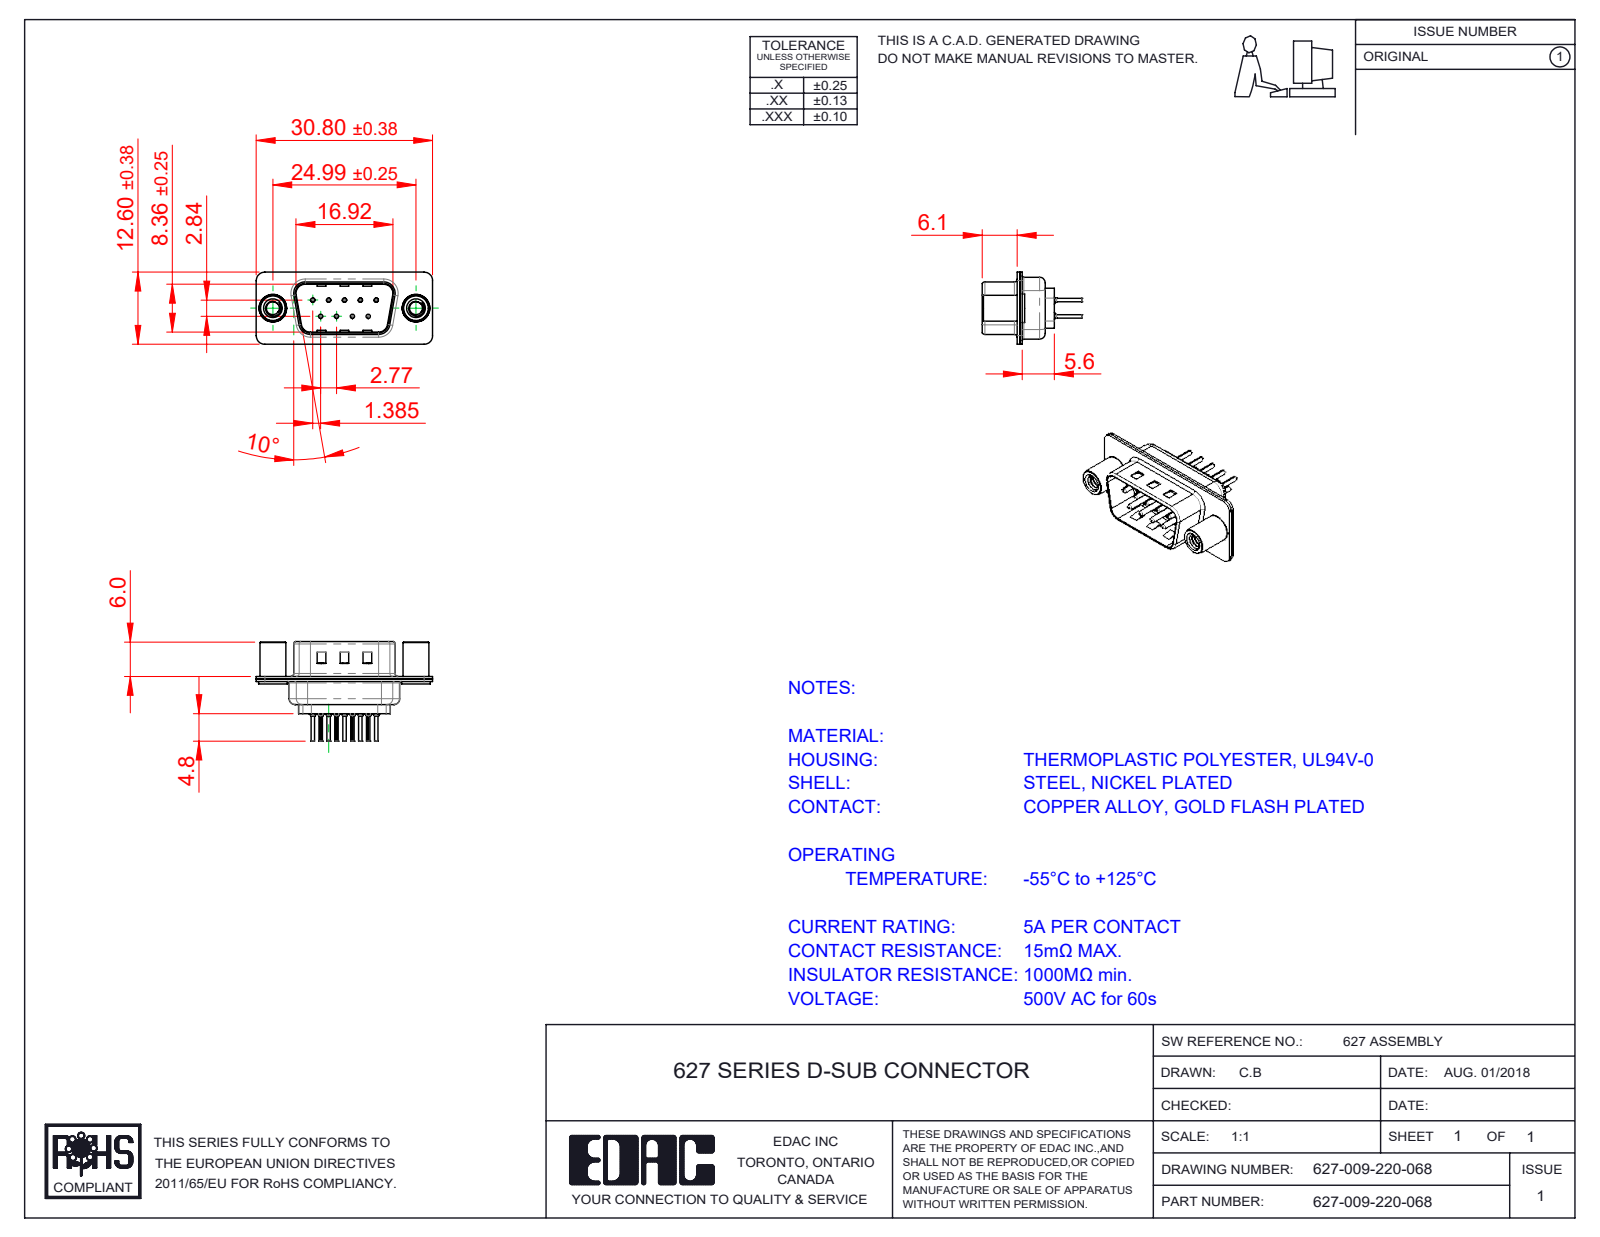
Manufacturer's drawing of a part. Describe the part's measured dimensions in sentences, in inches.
The part is named "627 Contact Row 1_20L; 627 Shell Rear_09 Contacts; 627 4-40 Threaded Standoff; 627 Housing_09 LP (+3 more)". Its 3-D file was written by "SolidWorks 2020 (CONFIG_CONTROL_DESIGN)". It is 14 solids with 1220 faces: 325 planar, 490 cylindrical and 405 other. Overall it measures 1.213 by 0.681 by 0.496 inches. Its volume is 0.084 cubic inches and its surface area 6.4 square inches. Round holes: 9 of diameter 0.008, 9 of diameter 0.014, 9 of diameter 0.043, 9 of diameter 0.063, 2 of diameter 0.089, 2 of diameter 0.157, 2 of diameter 0.189. Round bosses or shafts: 9 of diameter 0.079, 9 of diameter 0.059, 9 of diameter 0.03, 9 of diameter 0.024, 2 of diameter 0.197, 2 of diameter 0.193, 2 of diameter 0.177. Partial cylindrical surfaces (rounded edges, fillets, slot ends): 18 of radius 0.004, 18 of radius 0.059, 12 of radius 0.079, 8 of radius 0.02, 8 of radius 0.063, 4 of radius 0.01, 4 of radius 0.024, 4 of radius 0.026. The main face-to-face distances are 0.016, 0.018, 0.035, 0.032, 0.377, 0.055, 0.345, 0.02, 0.059, 0.22. The hole center spacings are 0.124, 0.109, 0.218, 0.198, 0.198, 0.327, 0.294, 0.295.
